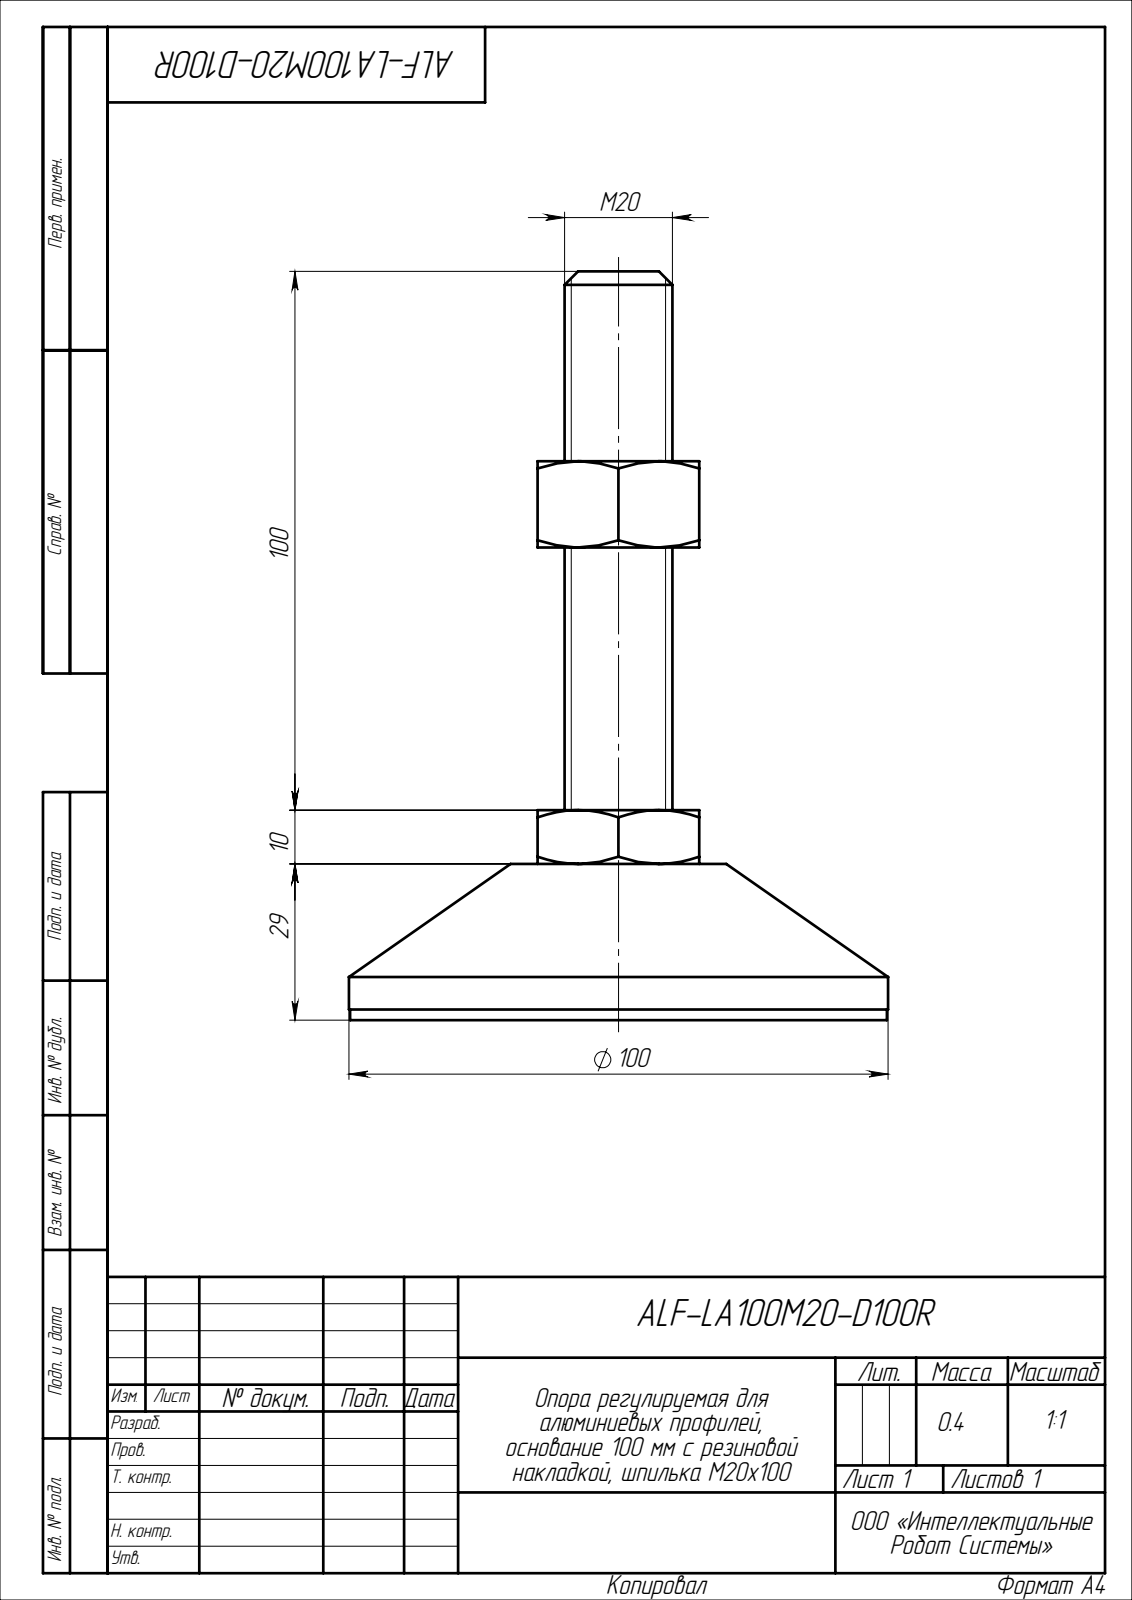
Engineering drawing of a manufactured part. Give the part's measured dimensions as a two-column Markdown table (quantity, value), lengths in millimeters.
| quantity | value |
| --- | --- |
| part name | ALF-LA100M20-D100R |
| STEP written by | SolidWorks 2022 (CONFIG_CONTROL_DESIGN) |
| units | millimeters |
| bodies | 1 solid, 55 faces (19 planar, 8 cylindrical, 28 other) |
| overall size | 139 × 100 × 100 |
| volume | 194 829 mm³ |
| surface area | 28 484 mm² |
| round bosses / shafts (diameter × count) | 100 × 1, 99.6 × 1, 20 × 1 |
| main face-to-face distances | 30, 29, 39, 10, 87.75, 58.75, 48.75, 103.75, 74.75, 64.75 |
